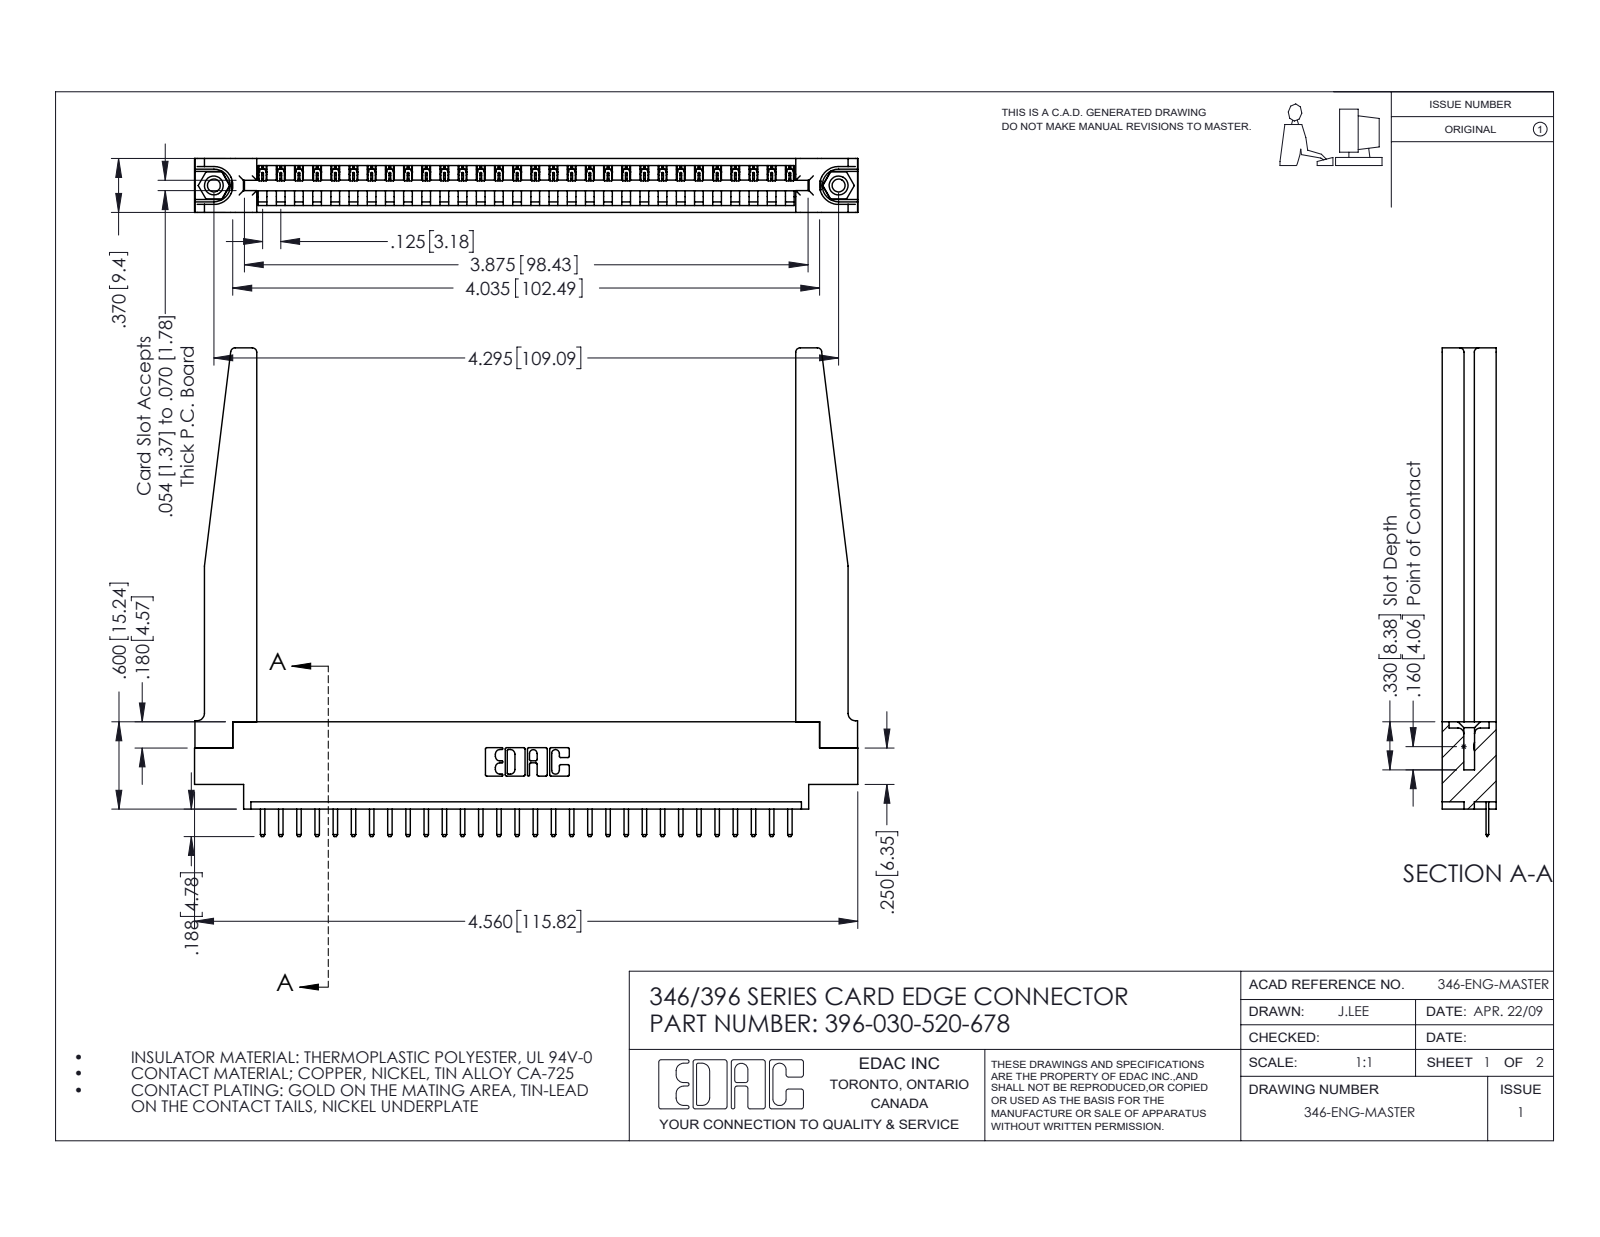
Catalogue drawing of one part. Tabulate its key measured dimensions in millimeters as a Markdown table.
| quantity | value |
| --- | --- |
| part name | 396-030-520-678; 346 Part_0.170 Offset - 0.156 Dia-TH; 345-250-001_345-250-001-102; 345-292-001_345-293-120 (+1 more) |
| STEP written by | SolidWorks 2016 (CONFIG_CONTROL_DESIGN) |
| units | millimeters |
| bodies | 35 solids, 2220 faces (1482 planar, 686 cylindrical, 52 other) |
| overall size | 115.8 × 85.3 × 9.4 |
| volume | 17 670 mm³ |
| surface area | 19 740 mm² |
| round holes (diameter × count) | 2.3 × 2, 3.2 × 2, 4 × 2, 1.6 × 1 |
| round bosses / shafts (diameter × count) | 3.9 × 2 |
| partial cylindrical surfaces (radius × count) | 0.3 × 62, 0.2 × 60, 0.3 × 22, 0.8 × 8, 0.2 × 6, 0.8 × 6, 0.7 × 3, 0.8 × 2 |
| main face-to-face distances | 9.4, 1.2, 8.2, 3.8, 1.8, 3.8, 6.4, 5.6, 2.5, 4.4 |
| hole center spacings | 6.2, 103.8, 109.1 |
